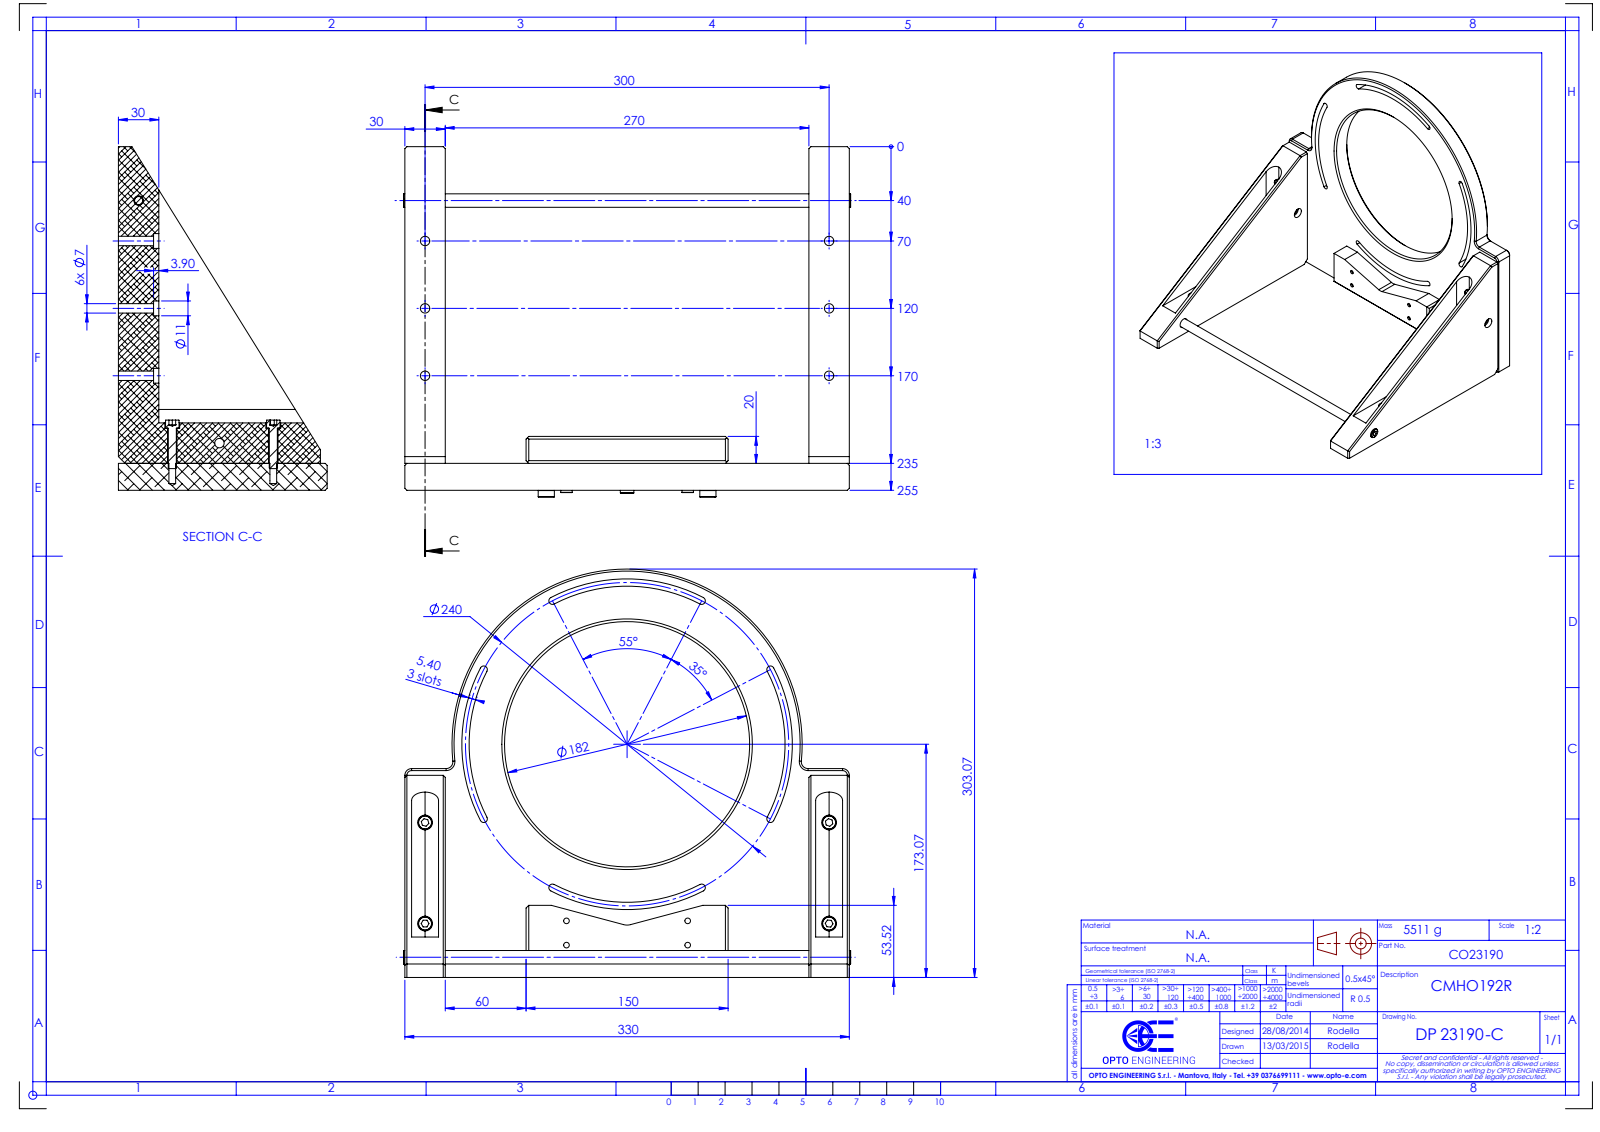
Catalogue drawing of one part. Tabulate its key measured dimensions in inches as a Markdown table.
| quantity | value |
| --- | --- |
| part name | DP23190-C_CMHO192R |
| STEP written by | SolidWorks 2021 (CONFIG_CONTROL_DESIGN) |
| units | inches |
| bodies | 0 solids, 308 faces (135 planar, 123 cylindrical, 50 other) |
| overall size | 13.071 × 11.932 × 10.236 |
| round holes (diameter × count) | 0.276 × 7, 0.433 × 7, 0.165 × 4, 0.394 × 4, 7.165 × 1 |
| round bosses / shafts (diameter × count) | 0.472 × 4, 0.394 × 4, 0.335 × 4 |
| partial cylindrical surfaces (radius × count) | 0.106 × 8, 0.197 × 4, 0.394 × 3, 4.618 × 1, 4.831 × 1, 5.118 × 1 |
| main face-to-face distances | 0.787, 11.811, 1.181, 0.197, 0.984, 12.992, 10.63, 12.008, 10.827, 12.795 |
| hole center spacings | 1.969, 11.811, 11.974, 0.709, 1.787, 1.833, 3.543, 3.613 |
